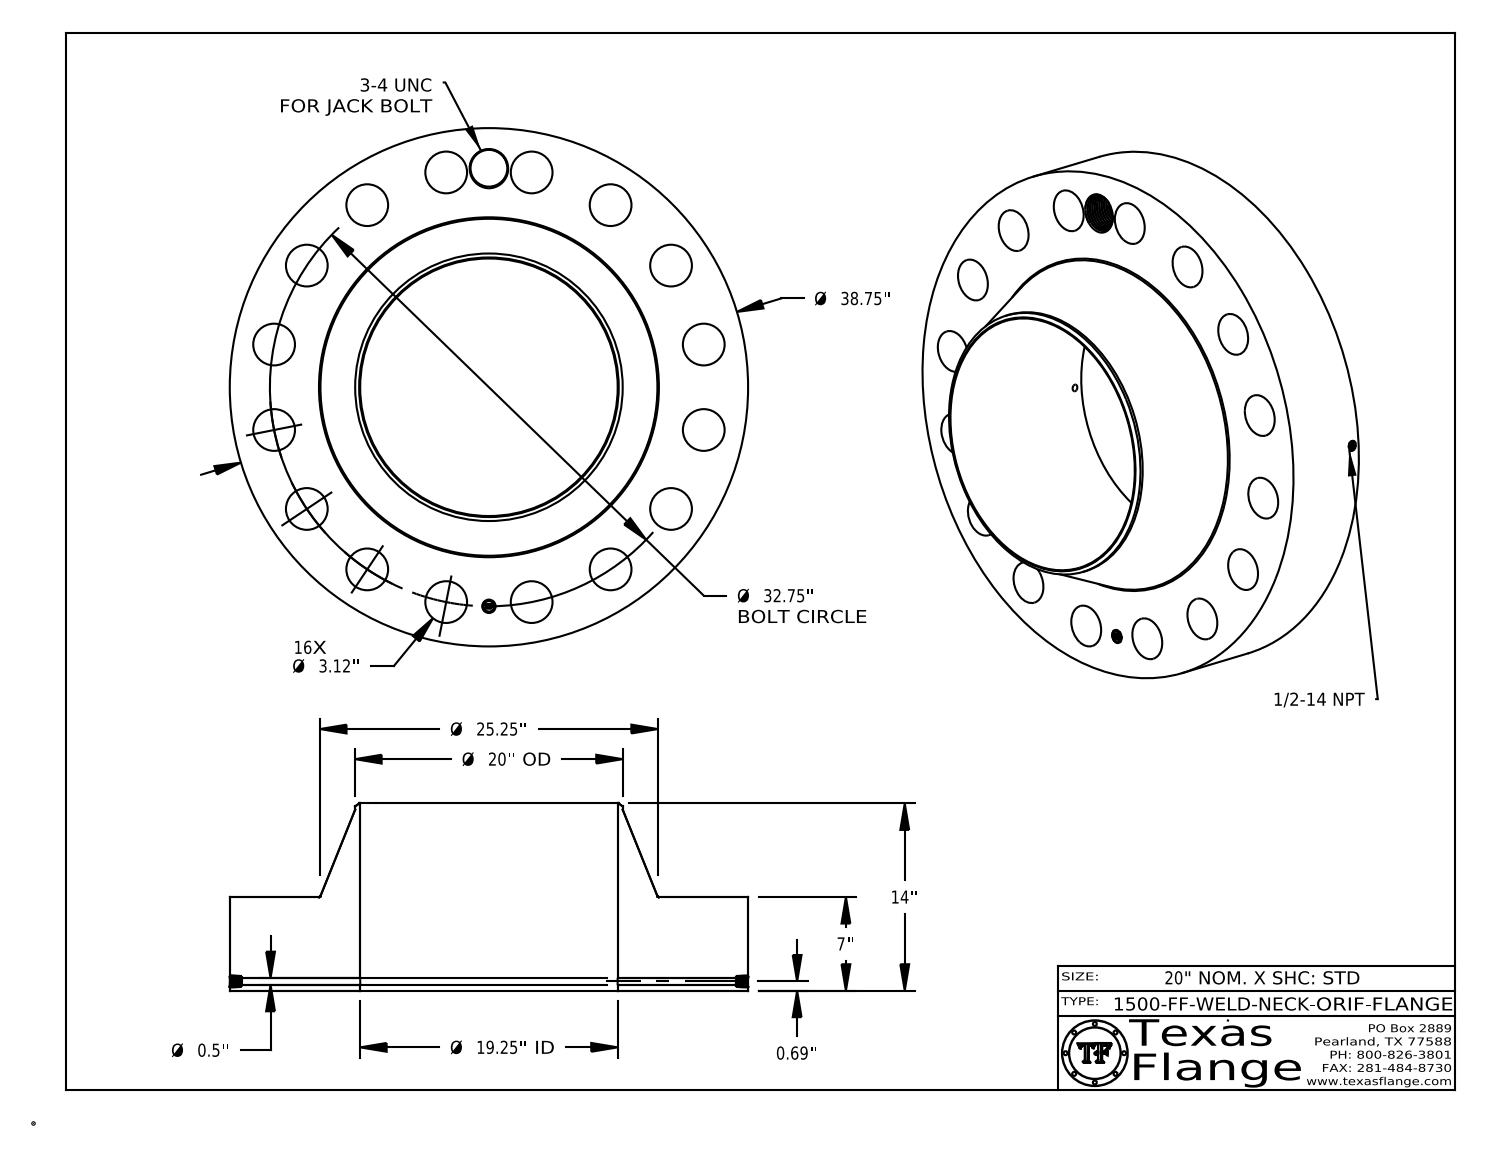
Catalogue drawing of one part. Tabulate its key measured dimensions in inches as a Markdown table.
| quantity | value |
| --- | --- |
| part name | 1500-FF-WELD-NECK |
| STEP written by | CATIA V5 STEP AP214 (AUTOMOTIVE_DESIGN) |
| units | inches |
| bodies | 1 solid, 860 faces (368 planar, 134 cylindrical, 358 other) |
| overall size | 38.75 × 38.75 × 14 |
| volume | 6 058 in³ |
| surface area | 4 771 in² |
| round holes (diameter × count) | 3.12 × 16, 0.5 × 1, 0.672 × 1, 1 × 1, 2.75 × 1, 19.25 × 1 |
| round bosses / shafts (diameter × count) | 0.061 × 8, 38.75 × 1, 20 × 1, 0.788 × 1 |
| main face-to-face distances | 7, 14, 0.015, 6.985, 7.015, 0.298, 0.292, 0.054, 0.248, 0.193 |
| hole center spacings | 30.257, 18.195, 27.231, 32.12, 16.375, 6.389, 6.389, 12.533 |
